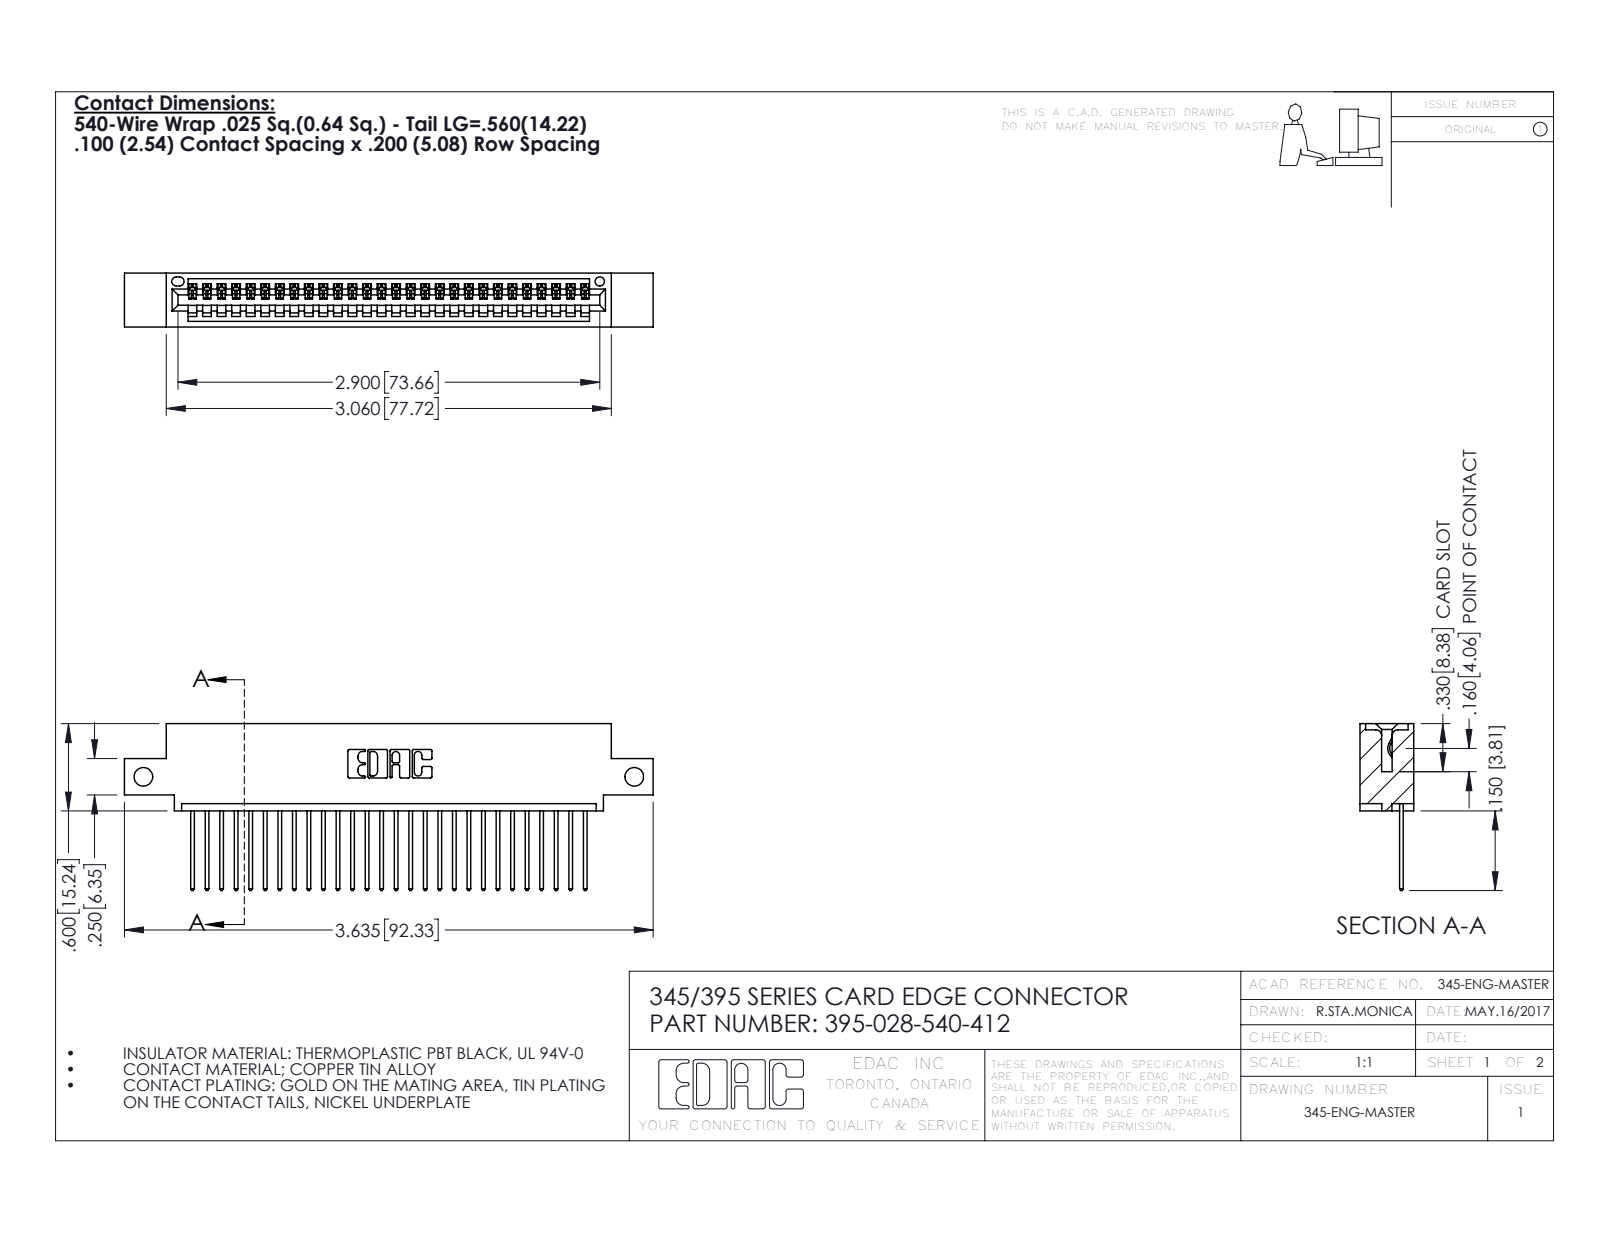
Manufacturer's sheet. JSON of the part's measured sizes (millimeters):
{"part_name": "395-028-540-412; 345-292-001_345-293-140; 345 Part_0.110 Offset - Side Mount", "step_written_by": "SolidWorks 2016 (CONFIG_CONTROL_DESIGN)", "units": "millimeters", "bodies": {"solids": 29, "faces": 1754, "planar": 1204, "cylindrical": 550, "other": 0}, "overall_size": [92.3, 29.1, 9.4], "volume_mm3": 8540, "surface_area_mm2": 11360, "round_holes": [[3.3, 2], [1.6, 1]], "partial_cylinders_radius": [[0.2, 56], [0.3, 56], [0.3, 22], [0.2, 6], [0.8, 6], [0.7, 3], [0.8, 2], [1, 2]], "face_to_face_distances": [7.6, 1.8, 9.4, 5.1, 2.5, 6.9, 0.6, 5.7, 3.8, 1.8], "hole_center_spacings": [85.7]}
